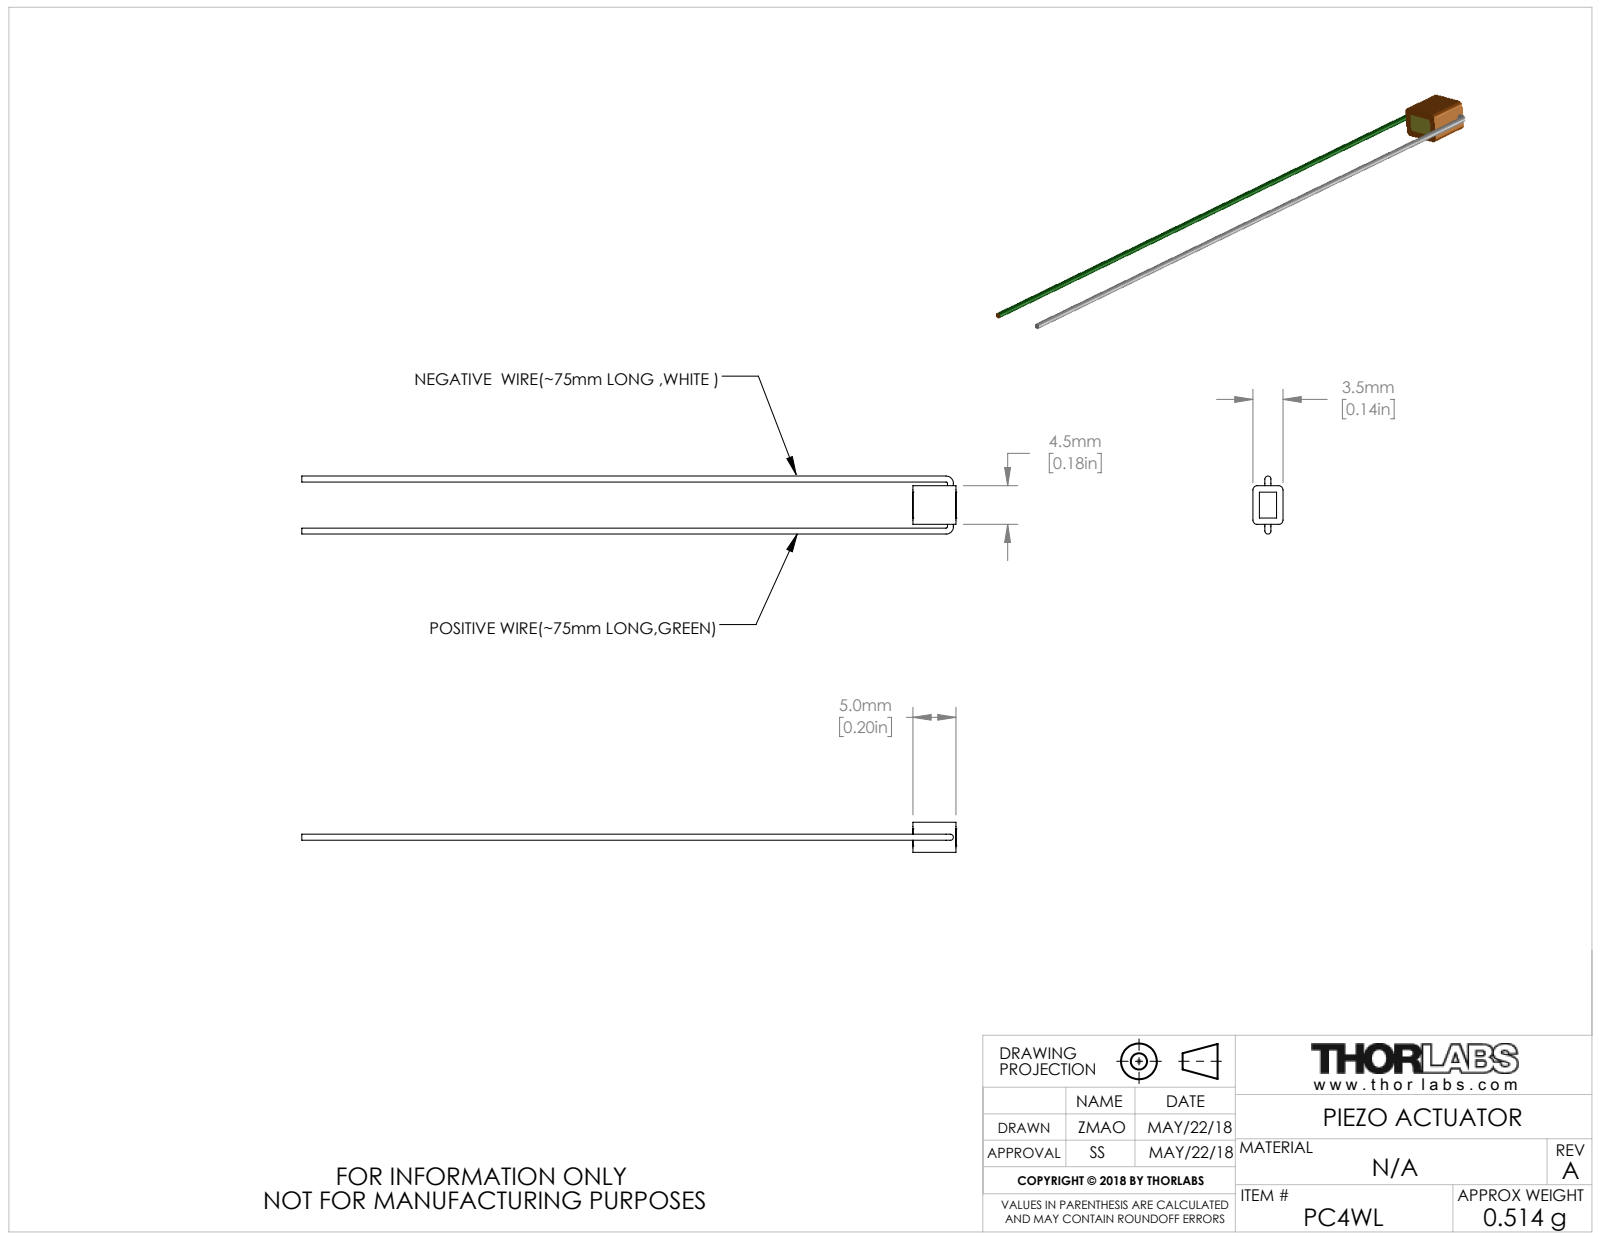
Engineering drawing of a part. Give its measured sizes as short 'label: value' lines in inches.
name: CTN012593
written by: SolidWorks 2016 (AUTOMOTIVE_DESIGN)
unit: in
bodies: 1 solid, 38 faces (18 planar, 16 cylindrical, 4 other)
size: 2.998 × 0.266 × 0.138
volume: 0.008 in³; area: 0.685 in²
bosses: 3× ⌀0.028
rounds: 4× R0.02
face distances: 0.138, 0.177, 0.197, 0.197, 0.198, 2.801, 2.801, 2.998, 2.998, 0.03
